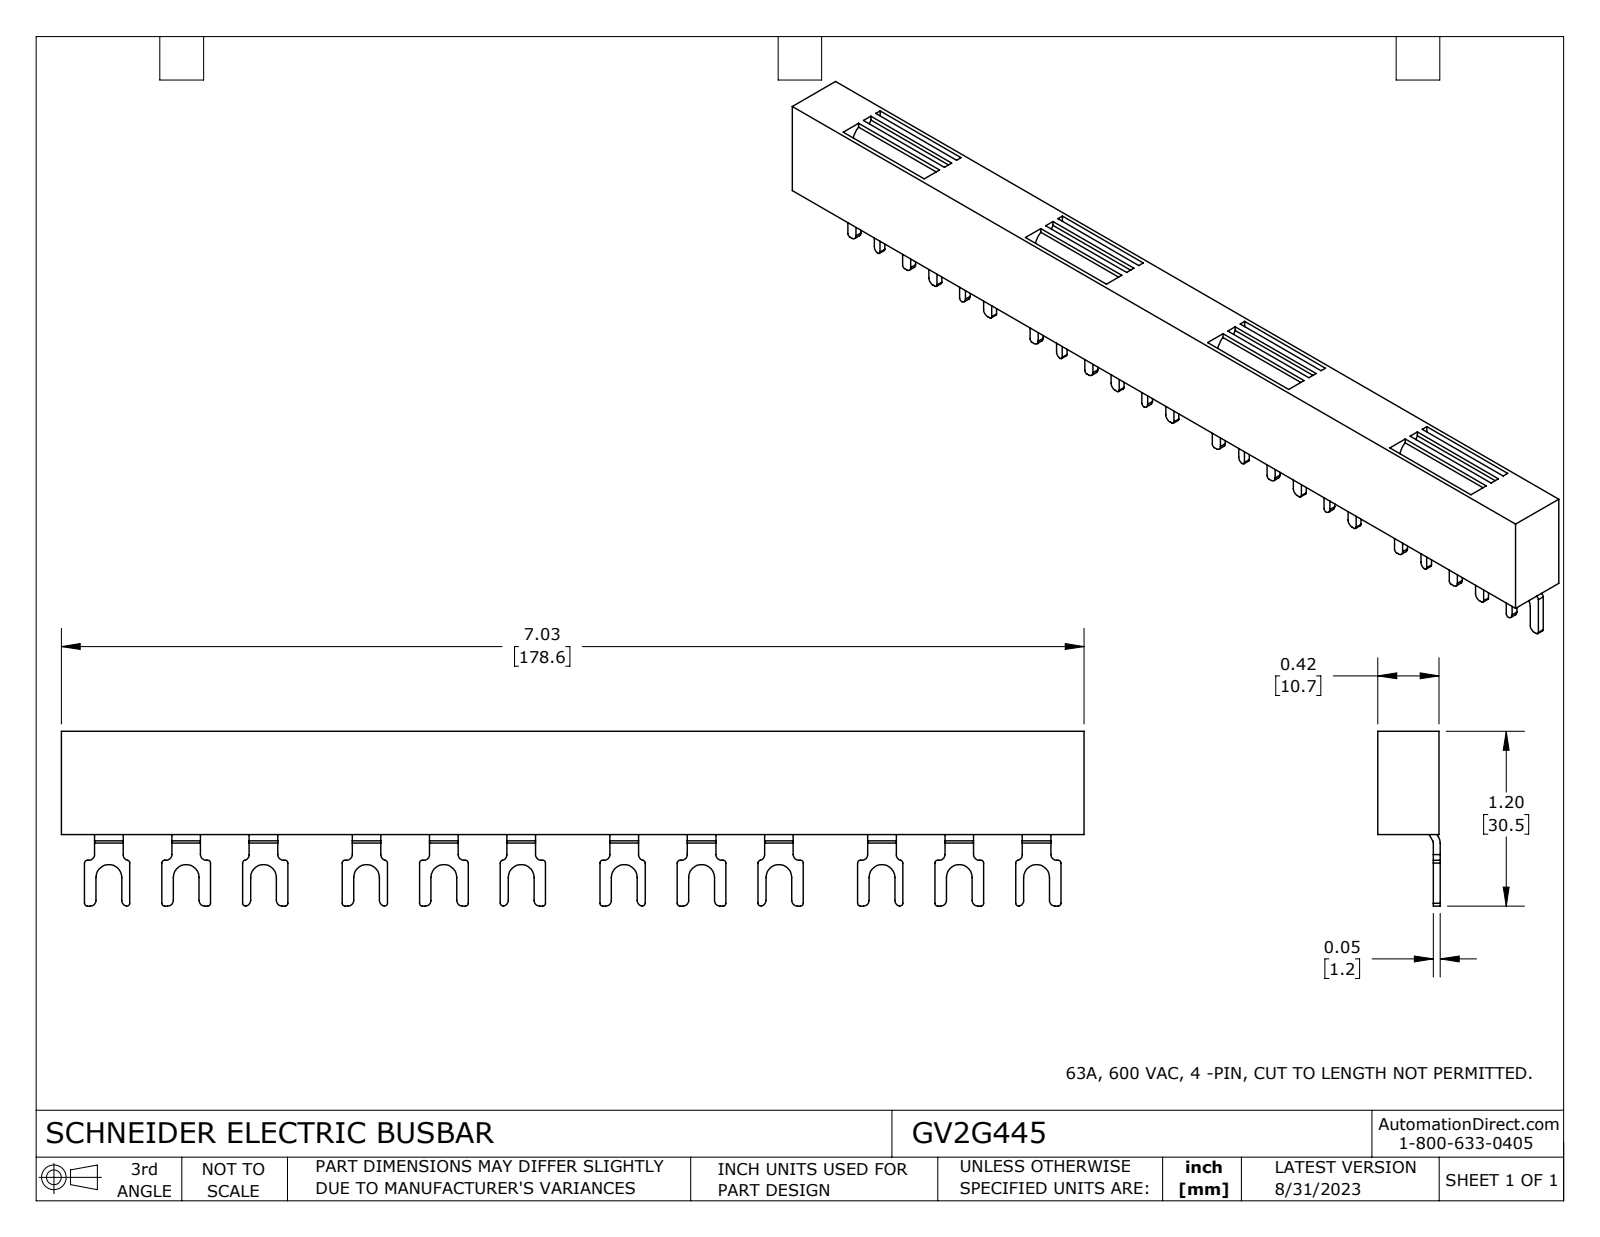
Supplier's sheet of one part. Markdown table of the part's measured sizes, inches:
| quantity | value |
| --- | --- |
| part name | GV2G445 |
| STEP written by | SolidWorks 2021 (CONFIG_CONTROL_DESIGN) |
| units | inches |
| bodies | 1 solid, 396 faces (254 planar, 142 cylindrical, 0 other) |
| overall size | 7.031 × 1.201 × 0.429 |
| volume | 2.084 in³ |
| surface area | 21.56 in² |
| partial cylindrical surfaces (radius × count) | 0.02 × 48, 0.039 × 48, 0.089 × 12, 0.031 × 1, 0.079 × 1, 0.098 × 1 |
| main face-to-face distances | 0.421, 0.709, 0.047, 0.039, 0.382, 0.429, 0.031, 0.39, 0.398, 0.35 |
